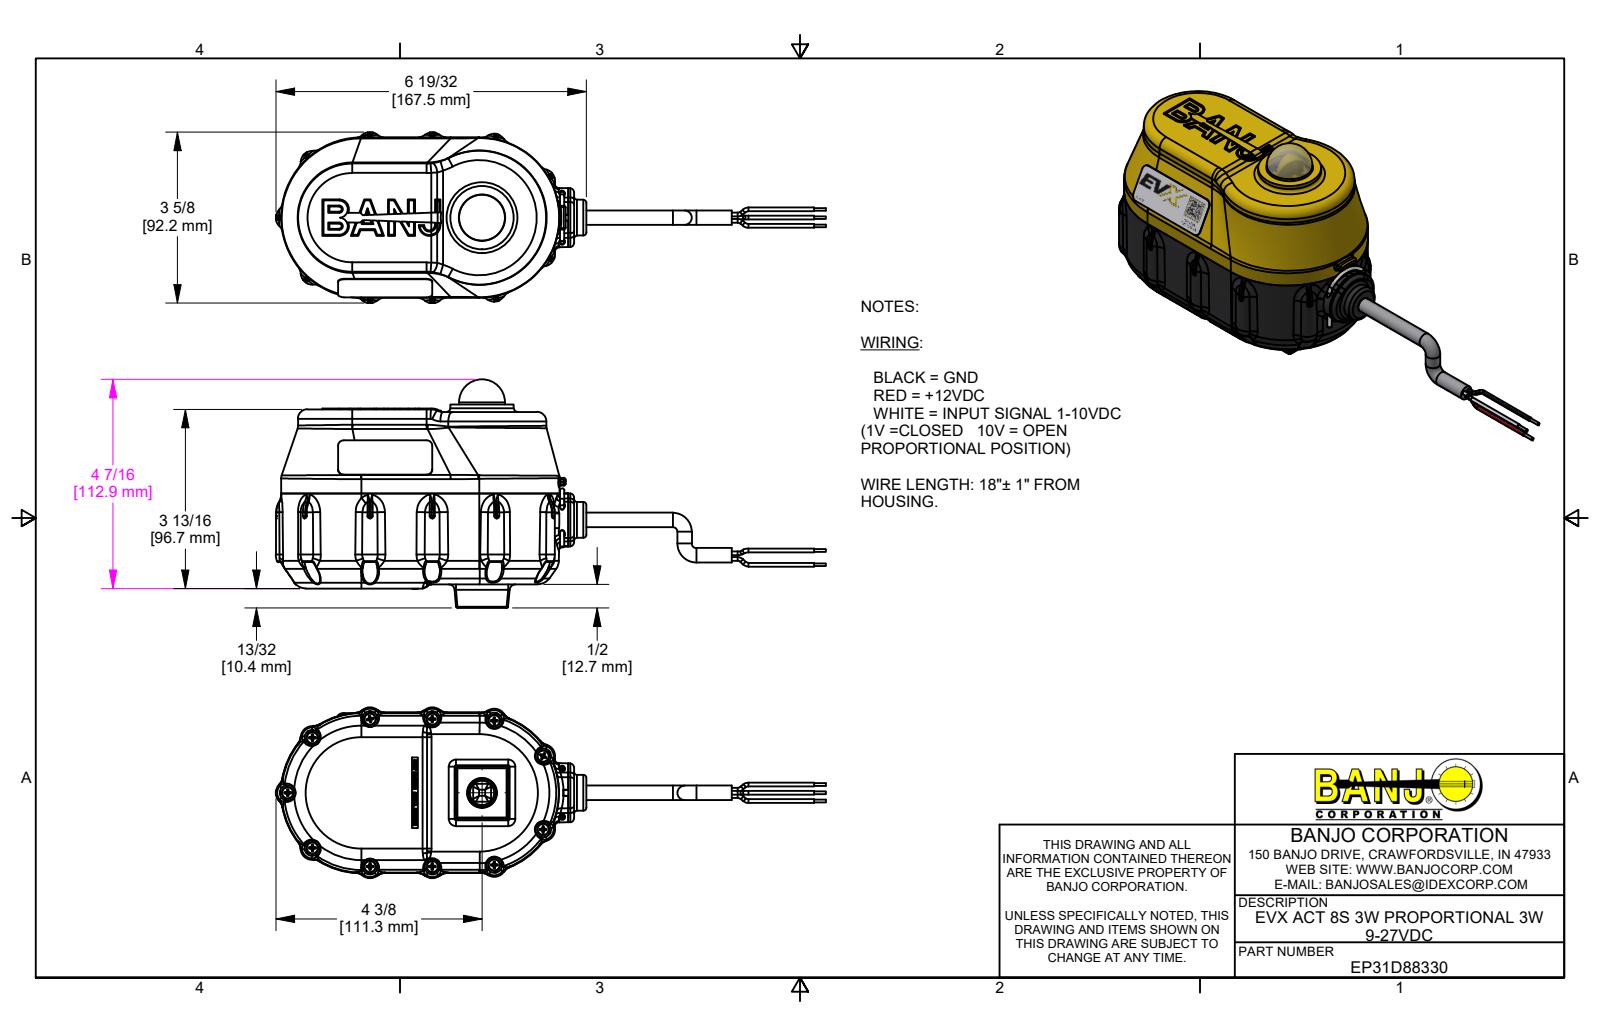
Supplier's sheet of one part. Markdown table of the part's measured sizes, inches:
| quantity | value |
| --- | --- |
| part name | EP31D88330; B61905PPHS; EP20KIT; EVP25102 (+8 more) |
| STEP written by | Autodesk Inventor 2022 (AUTOMOTIVE_DESIGN) |
| units | inches |
| bodies | 600 solids, 16973 faces (6541 planar, 5795 cylindrical, 4637 other) |
| overall size | 11.685 × 4.853 × 3.63 |
| volume | 30.76 in³ |
| surface area | 435.7 in² |
| round holes (diameter × count) | 0.01 × 184, 0.009 × 27, 0.012 × 27, 0.029 × 12, 0.019 × 11, 0.095 × 11, 0.15 × 11, 0.076 × 10, 0.033 × 7, 0.017 × 6, 0.067 × 6, 0.097 × 4 |
| round bosses / shafts (diameter × count) | 0.026 × 167, 0.028 × 27, 0.25 × 17, 0.08 × 15, 0.14 × 11, 0.108 × 11, 0.085 × 11, 0.043 × 11 |
| partial cylindrical surfaces (radius × count) | 0.04 × 152, 0.02 × 85, 0.01 × 76, 0.005 × 74, 0.004 × 52, 0.015 × 32, 0.008 × 28, 0.08 × 28 |
| main face-to-face distances | 0.078, 0.076, 0.1, 2.565, 1.417, 0.08, 0.615, 0.537, 0.617, 0.539 |
| hole center spacings | 1.283, 2.73, 2.967, 3.45, 0.487, 0.492, 0.668, 0.674 |
